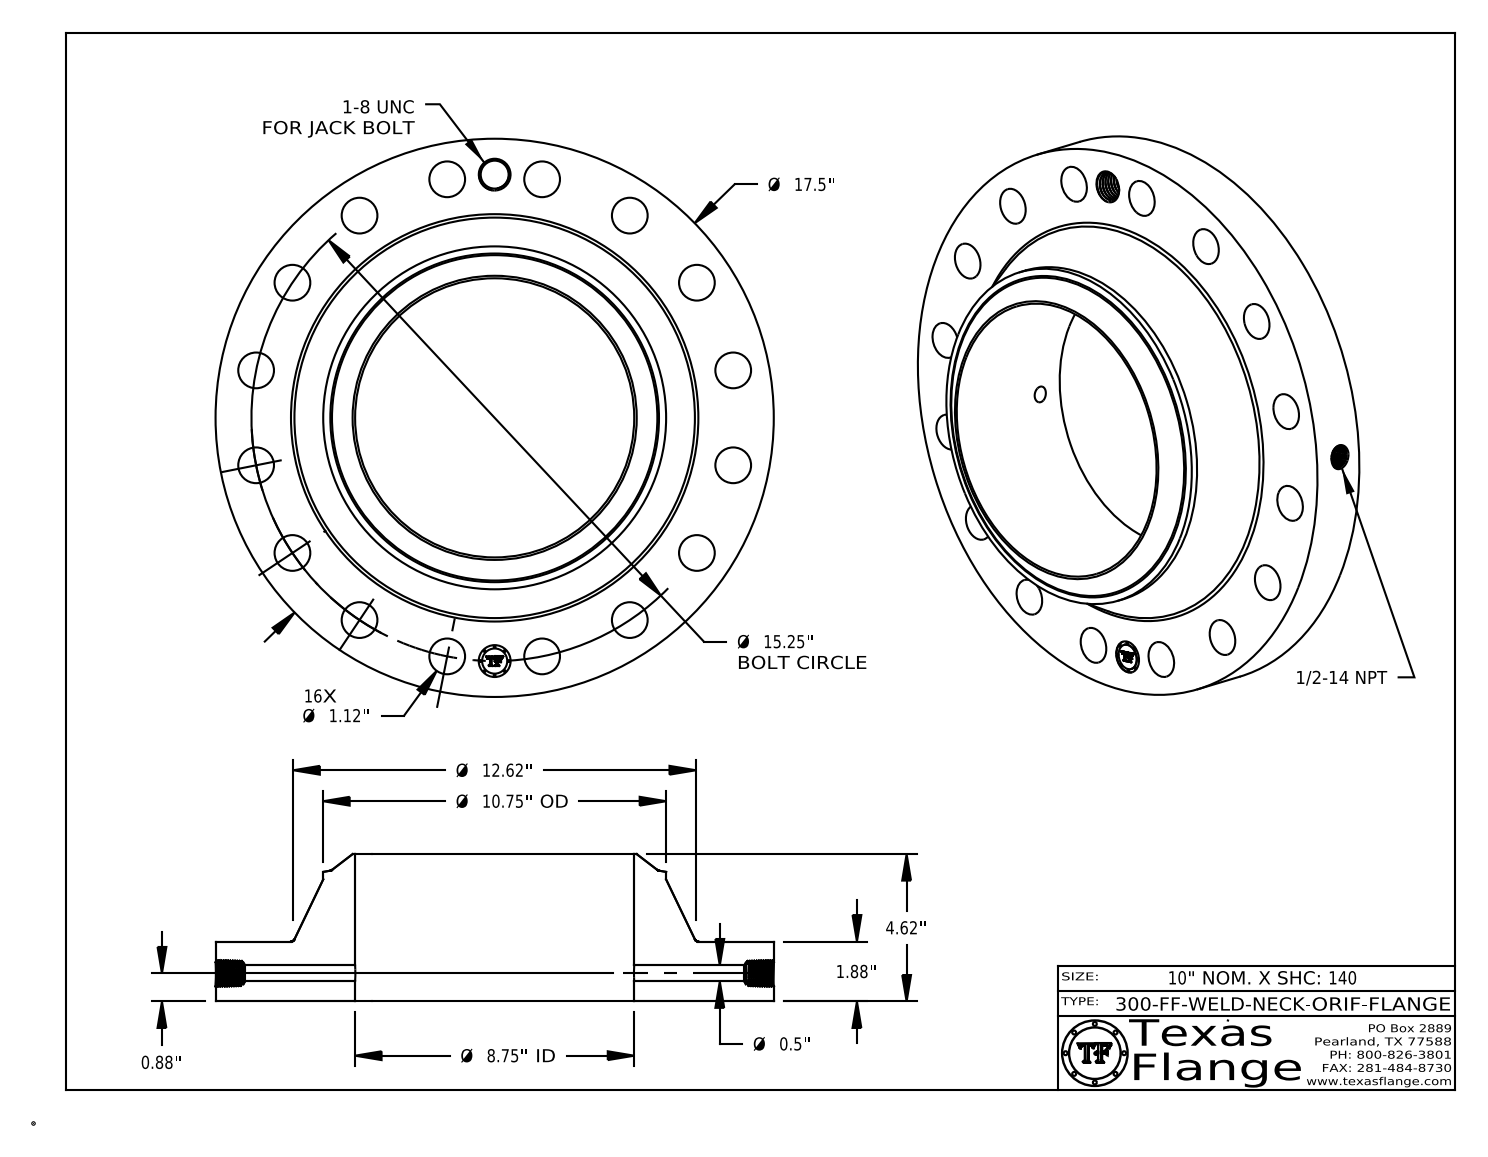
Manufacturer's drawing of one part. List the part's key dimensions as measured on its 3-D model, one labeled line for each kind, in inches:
Part name (STEP PRODUCT): 300-FF-WELD-NECK
STEP written by: CATIA V5 STEP AP214 (AUTOMOTIVE_DESIGN)
Units: inches
Bodies: 1 solid, 788 faces (368 planar, 107 cylindrical, 313 other)
Overall size (bounding box): 17.5 × 17.5 × 4.62
Volume: 412.8 in³ · Surface area: 746.7 in²
Round holes (diameter × count): ⌀1.12 ×16, ⌀0.5 ×1, ⌀0.672 ×1, ⌀0.875 ×1, ⌀1 ×1, ⌀8.75 ×1
Round bosses / shafts (diameter × count): ⌀0.061 ×8, ⌀17.5 ×1, ⌀10.75 ×1, ⌀0.788 ×1
Main face-to-face distances: 1.88, 4.62, 2.74, 0.015, 1.865, 2.755, 0.298, 0.292, 0.054, 0.248
Hole centre spacings: 5.836, 7.625, 10.783, 14.089, 14.957, 2.975, 2.975, 8.472
